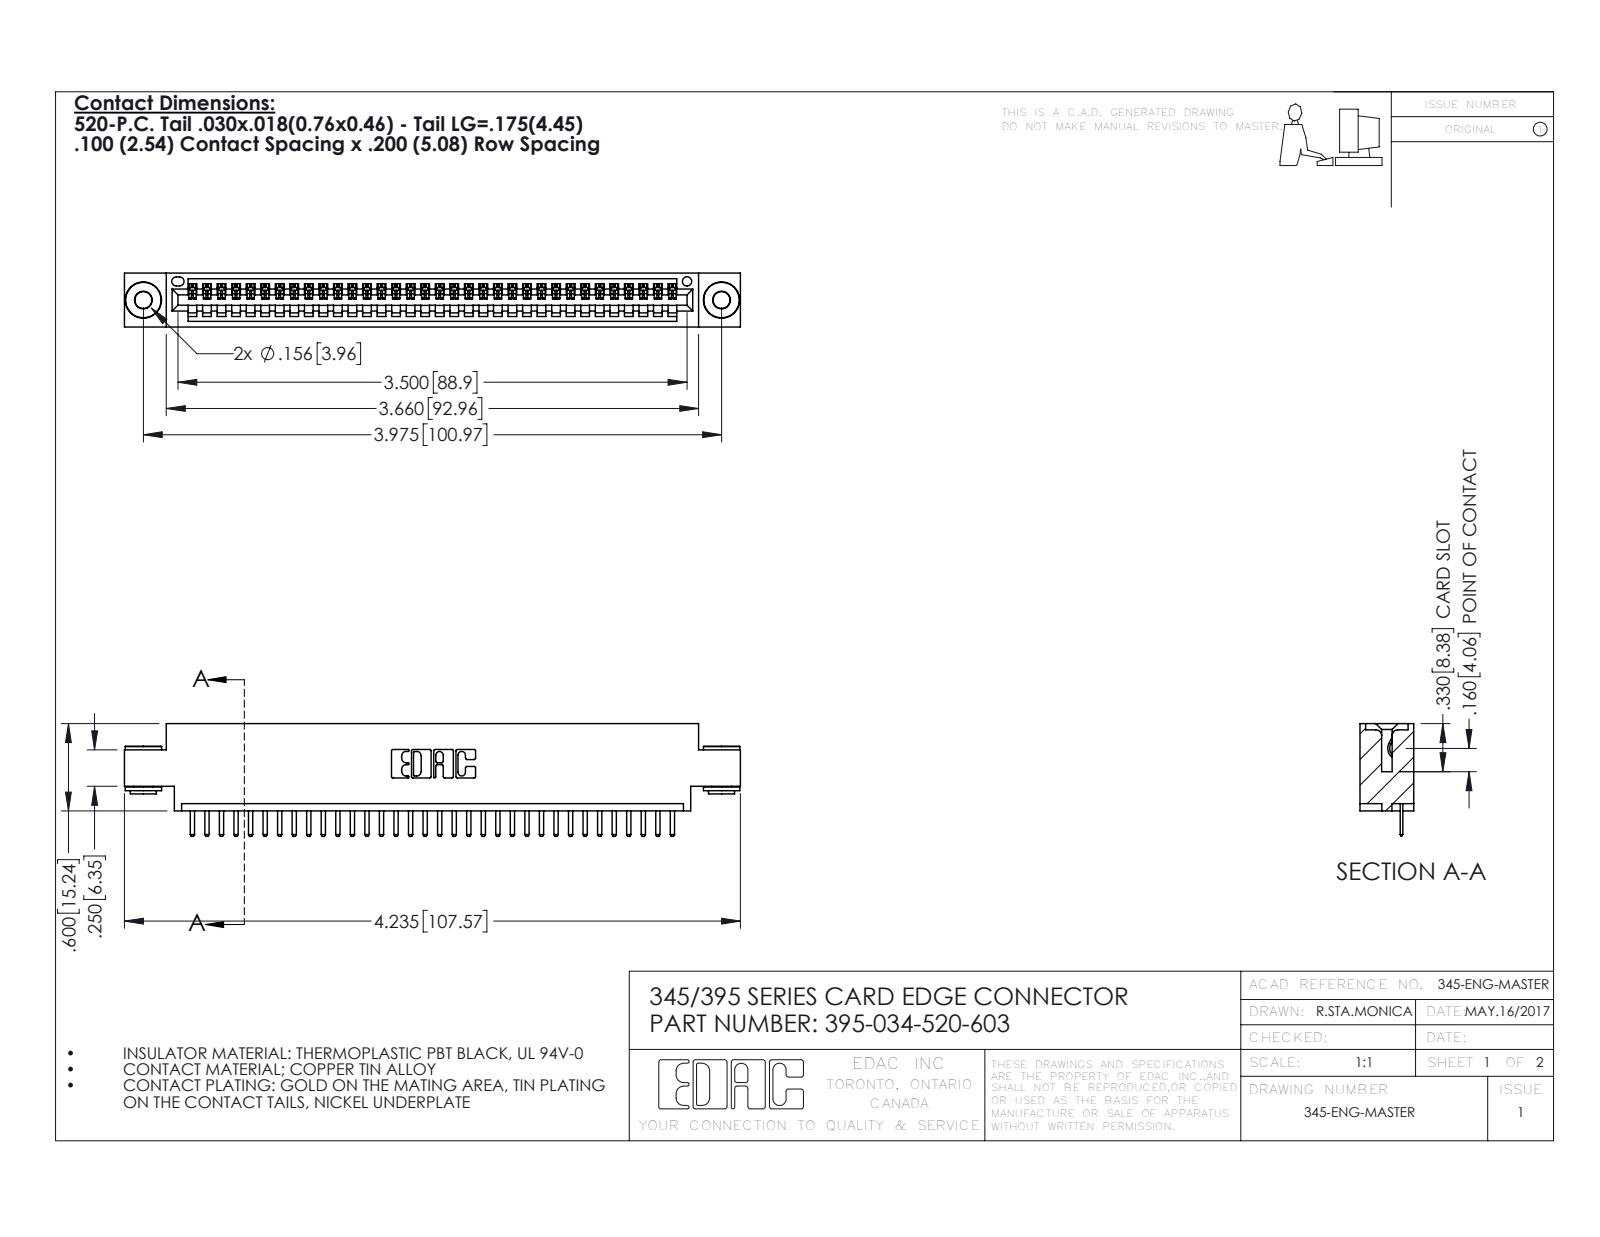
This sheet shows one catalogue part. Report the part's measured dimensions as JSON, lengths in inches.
{"part_name": "395-034-520-603; 345 Part_0.170 Offset - 0.156 Dia-TH; 345-250-002_345-250-002-102; 345-292-001_345-293-120", "step_written_by": "SolidWorks 2016 (CONFIG_CONTROL_DESIGN)", "units": "inches", "bodies": {"solids": 37, "faces": 2276, "planar": 1522, "cylindrical": 746, "other": 8}, "overall_size": [4.235, 0.775, 0.37], "volume_in3": 0.608, "surface_area_in2": 20.38, "round_holes": [[0.116, 2], [0.156, 2], [0.064, 1]], "round_bosses_or_shafts": [[0.25, 2], [0.18, 2], [0.136, 2]], "partial_cylinders_radius": [[0.01, 70], [0.006, 68], [0.01, 22], [0.007, 6], [0.031, 6], [0.026, 3], [0.031, 2], [0.04, 2]], "face_to_face_distances": [0.072, 0.298, 0.37, 0.2, 0.098, 0.272, 0.025, 0.225, 0.175, 0.072], "hole_center_spacings": [0.27, 3.74, 3.975]}
